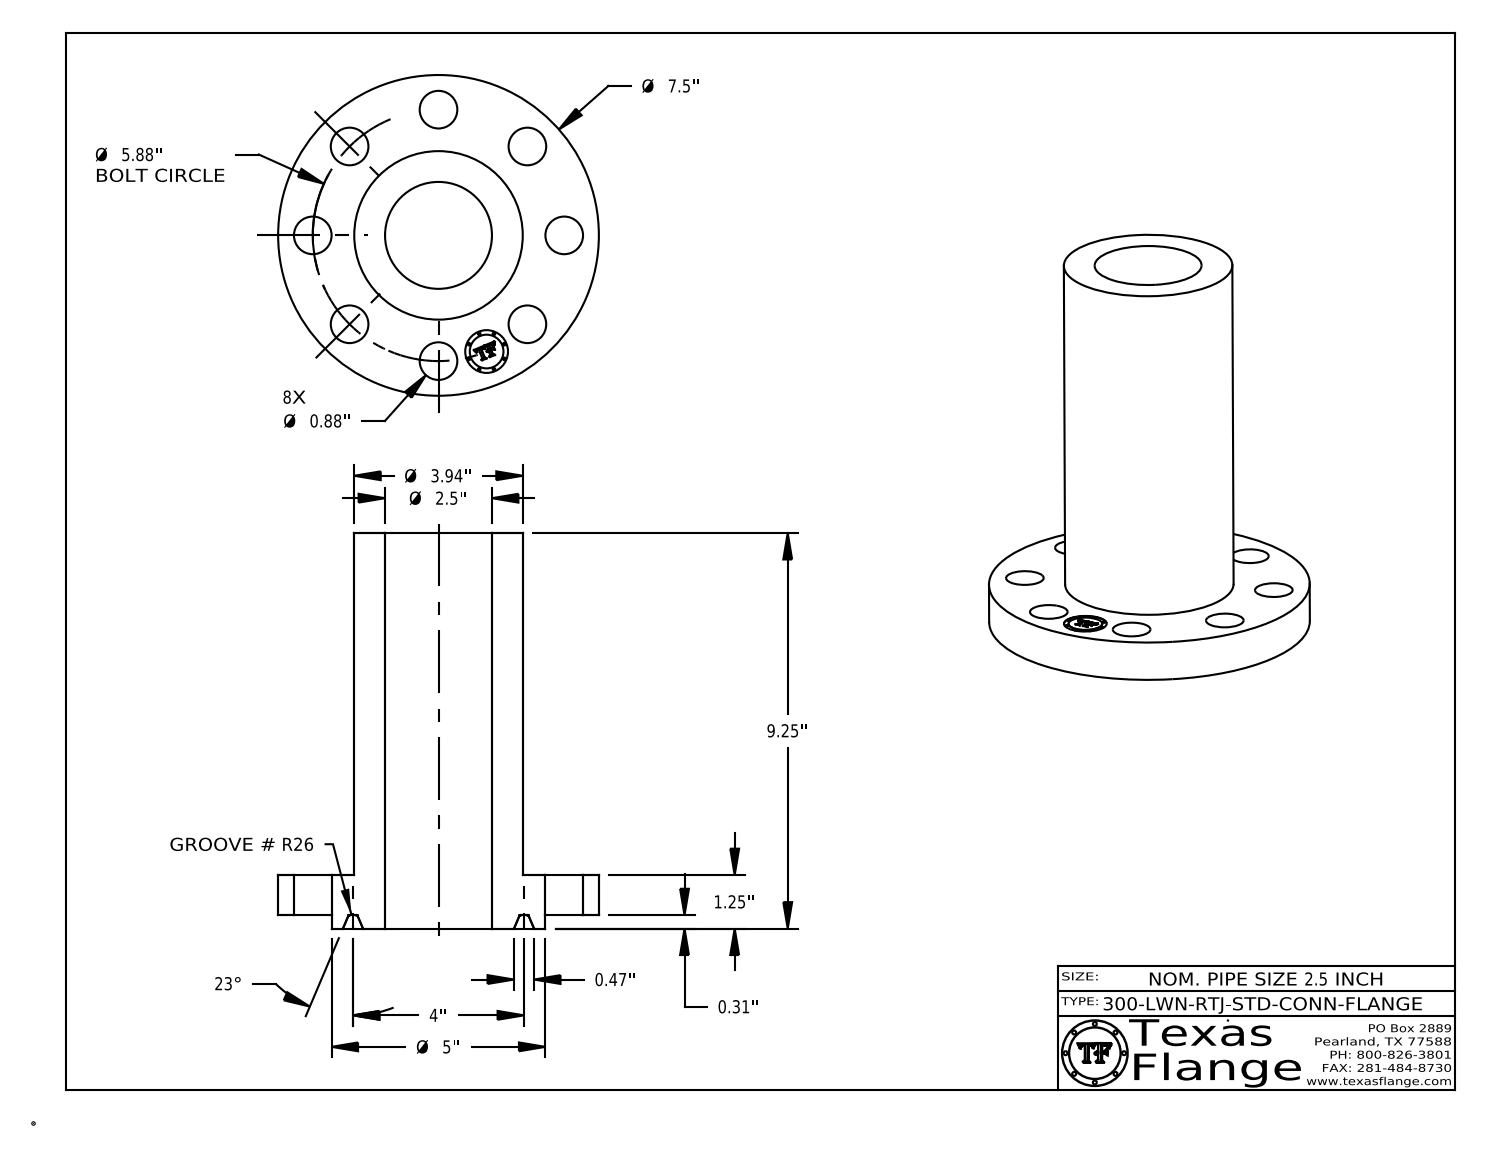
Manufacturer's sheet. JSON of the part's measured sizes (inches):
{"part_name": "2.5-300-LWN-RTJ-STD-CONN-FLANGE", "step_written_by": "CATIA V5 STEP AP214 (AUTOMOTIVE_DESIGN)", "units": "inches", "bodies": {"solids": 1, "faces": 423, "planar": 371, "cylindrical": 44, "other": 8}, "overall_size": [9.251, 7.5, 7.5], "volume_in3": 93.81, "surface_area_in2": 293.4, "round_holes": [[0.88, 8], [1, 1], [2.5, 1]], "round_bosses_or_shafts": [[0.061, 8], [7.5, 1], [5, 1], [3.94, 1], [0.788, 1]], "face_to_face_distances": [0.937, 0.313, 1.25, 9.25, 8.937, 8, 1.246, 0.933, 8.005, 0.019], "hole_center_spacings": [2.25, 5.432, 2.94, 2.94, 4.157, 4.158, 3.267, 5.88]}
